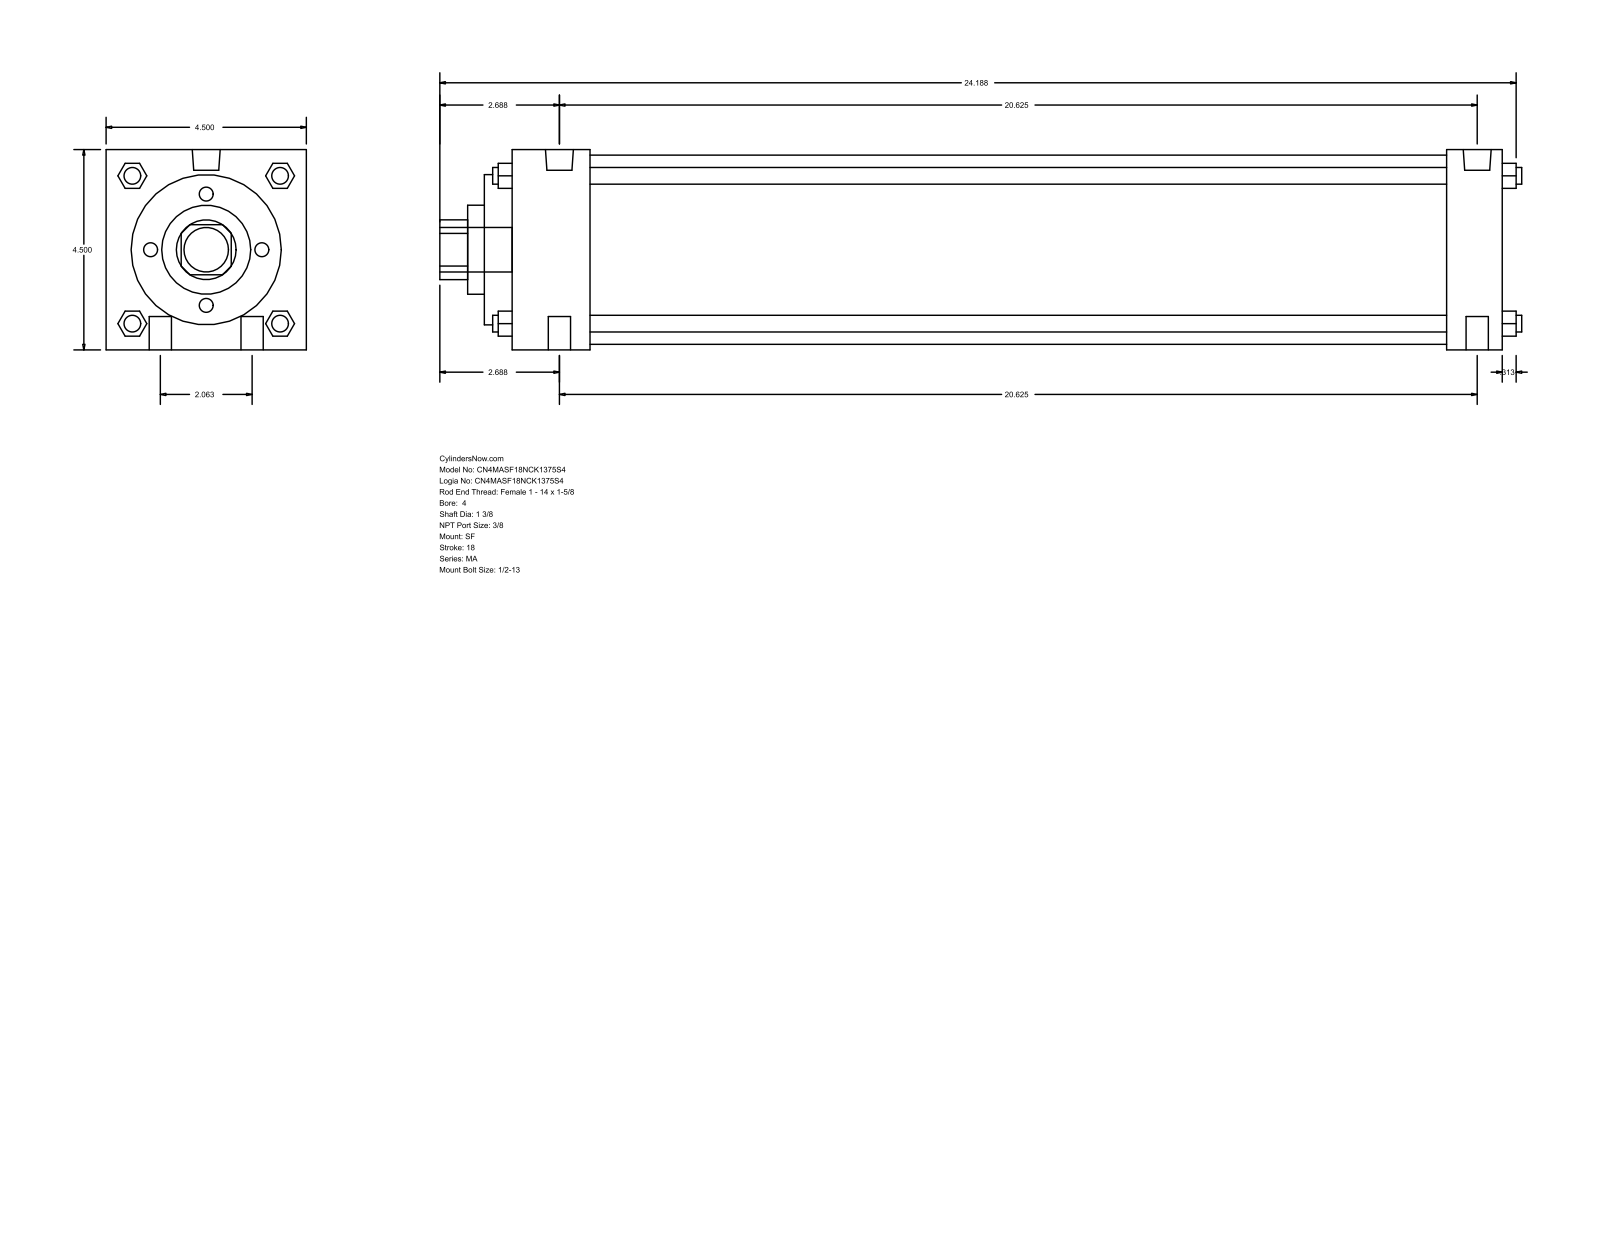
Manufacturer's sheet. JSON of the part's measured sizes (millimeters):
{"part_name": "MA_SF__0400_1.375", "step_written_by": "GSSL Pune (CONFIG_CONTROL_DESIGN)", "units": "millimeters", "bodies": {"solids": 0, "faces": 126, "planar": 95, "cylindrical": 31, "other": 0}, "overall_size": [617.54, 114.3, 114.3], "round_holes": [[34.92, 1], [50.8, 1], [85.72, 1], [107.95, 1]], "round_bosses_or_shafts": [[12.7, 4], [9.53, 4], [15.93, 2], [11.11, 2], [25.4, 1]], "partial_cylinders_radius": [[17.06, 1]], "face_to_face_distances": [114.3, 565.15, 581.02, 15.87, 549.27, 533.4, 31.75, 60.32, 44.45, 488.95]}
